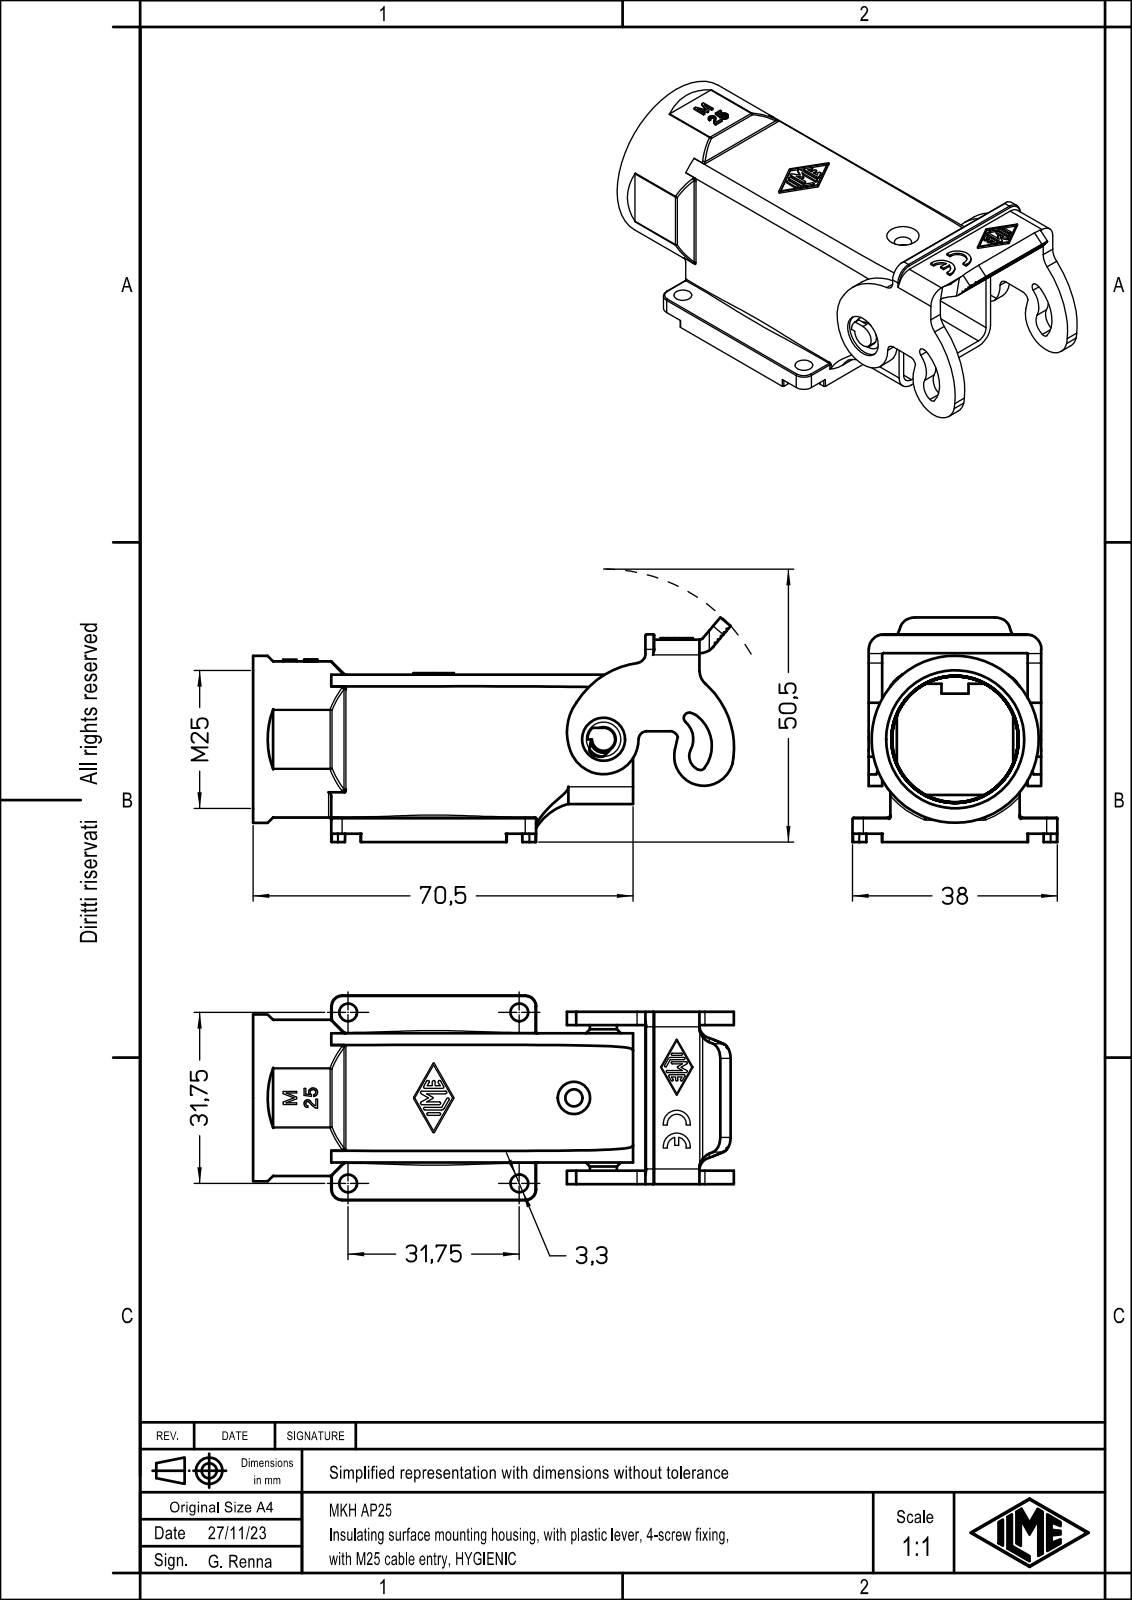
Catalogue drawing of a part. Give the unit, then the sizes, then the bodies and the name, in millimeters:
Units: millimetres
Overall size (bounding box): 89.2 × 41.69 × 38
Round holes (diameter × count): ⌀3.3 ×4, ⌀3.2 ×1, ⌀8 ×1, ⌀23.6 ×1
Round bosses / shafts (diameter × count): ⌀31 ×1, ⌀5 ×1, ⌀4.3 ×1
Partial cylindrical surfaces — rounded edges, fillets, slot ends (radius × count): R0.2 ×51, R0.5 ×16, R2 ×16, R0.25 ×15, R0.1 ×7, R3.2 ×7, R2.8 ×6, R0.3 ×4
Main face-to-face distances: 1.2, 22.8, 2.5, 24, 28, 29.5, 4, 1.5, 21.6, 26.8
Hole centre spacings: 31.75, 44.78, 44.9, 18.82, 18.83
Volume: 19 475 mm³ · Surface area: 19 587 mm²
Bodies: 1 solid, 644 faces (334 planar, 207 cylindrical, 103 other)
Part name (STEP PRODUCT): MKH AP25
STEP written by: Creo Elements/Direct Modeling 20.1B 02-Apr-2019 (C) Parametric Technology GmbH (AUTOMOTIVE_DESIGN)
